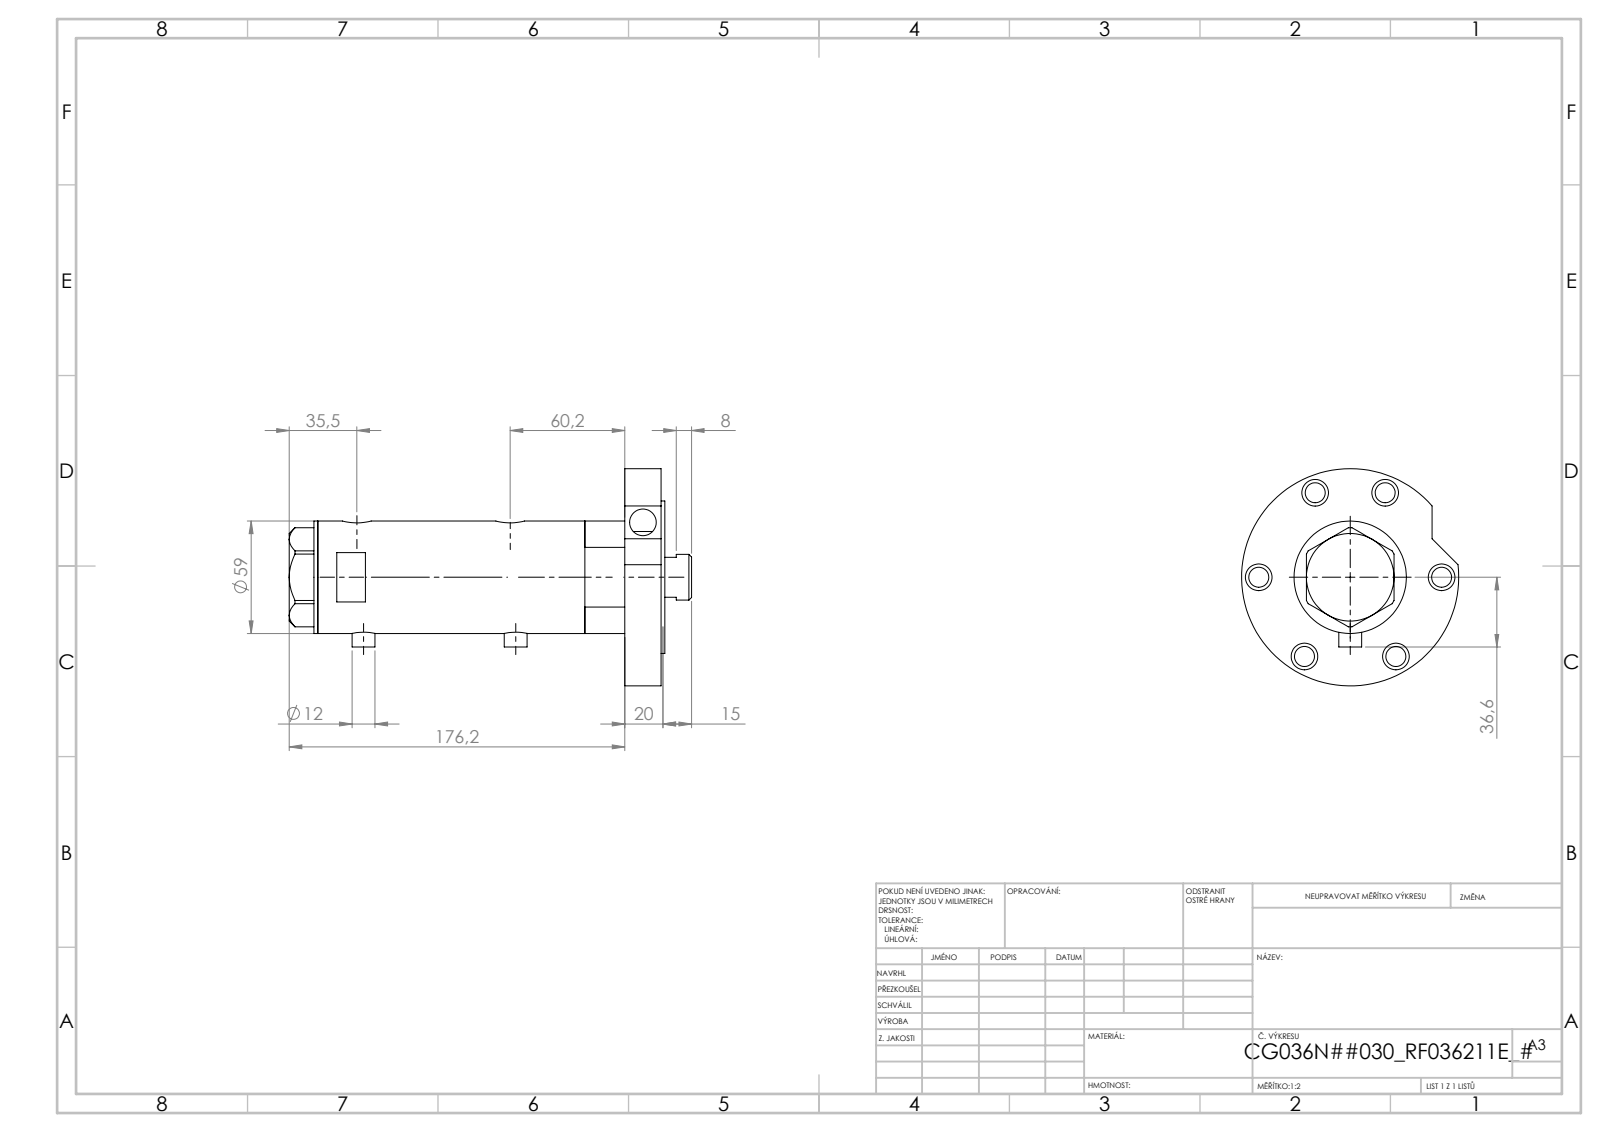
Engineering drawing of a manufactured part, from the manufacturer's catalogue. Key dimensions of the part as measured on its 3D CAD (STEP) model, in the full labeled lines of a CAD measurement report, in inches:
Part name (STEP PRODUCT): V270CG_BACK; V270CG_FRONT; V270CG_VC; V270CG_RF211E (+1 more)
STEP written by: SolidWorks 2019 (CONFIG_CONTROL_DESIGN)
Units: inches
Bodies: 5 solids, 170 faces (64 planar, 86 cylindrical, 20 other)
Overall size (bounding box): 7.615 × 4.488 × 4.488
Volume: 35 in³ · Surface area: 196.3 in²
Round holes (diameter × count): ⌀0.551 ×7, ⌀0.413 ×6, ⌀0.197 ×2, ⌀0.383 ×2, ⌀0.492 ×2, ⌀0.591 ×2, ⌀0.335 ×1, ⌀0.984 ×1, ⌀1.043 ×1, ⌀1.417 ×1, ⌀1.575 ×1, ⌀1.89 ×1
Round bosses / shafts (diameter × count): ⌀0.472 ×2, ⌀4.488 ×1, ⌀3.15 ×1, ⌀2.323 ×1, ⌀1.811 ×1, ⌀0.945 ×1
Main face-to-face distances: 0.748, 0.079, 6.372, 0.827, 5.545, 6.293, 3.439, 2.106, 2.854, 2.933
Hole centre spacings: 1.89, 0.114, 0.138, 2.1, 2.447, 2.561, 2.585, 2.699
